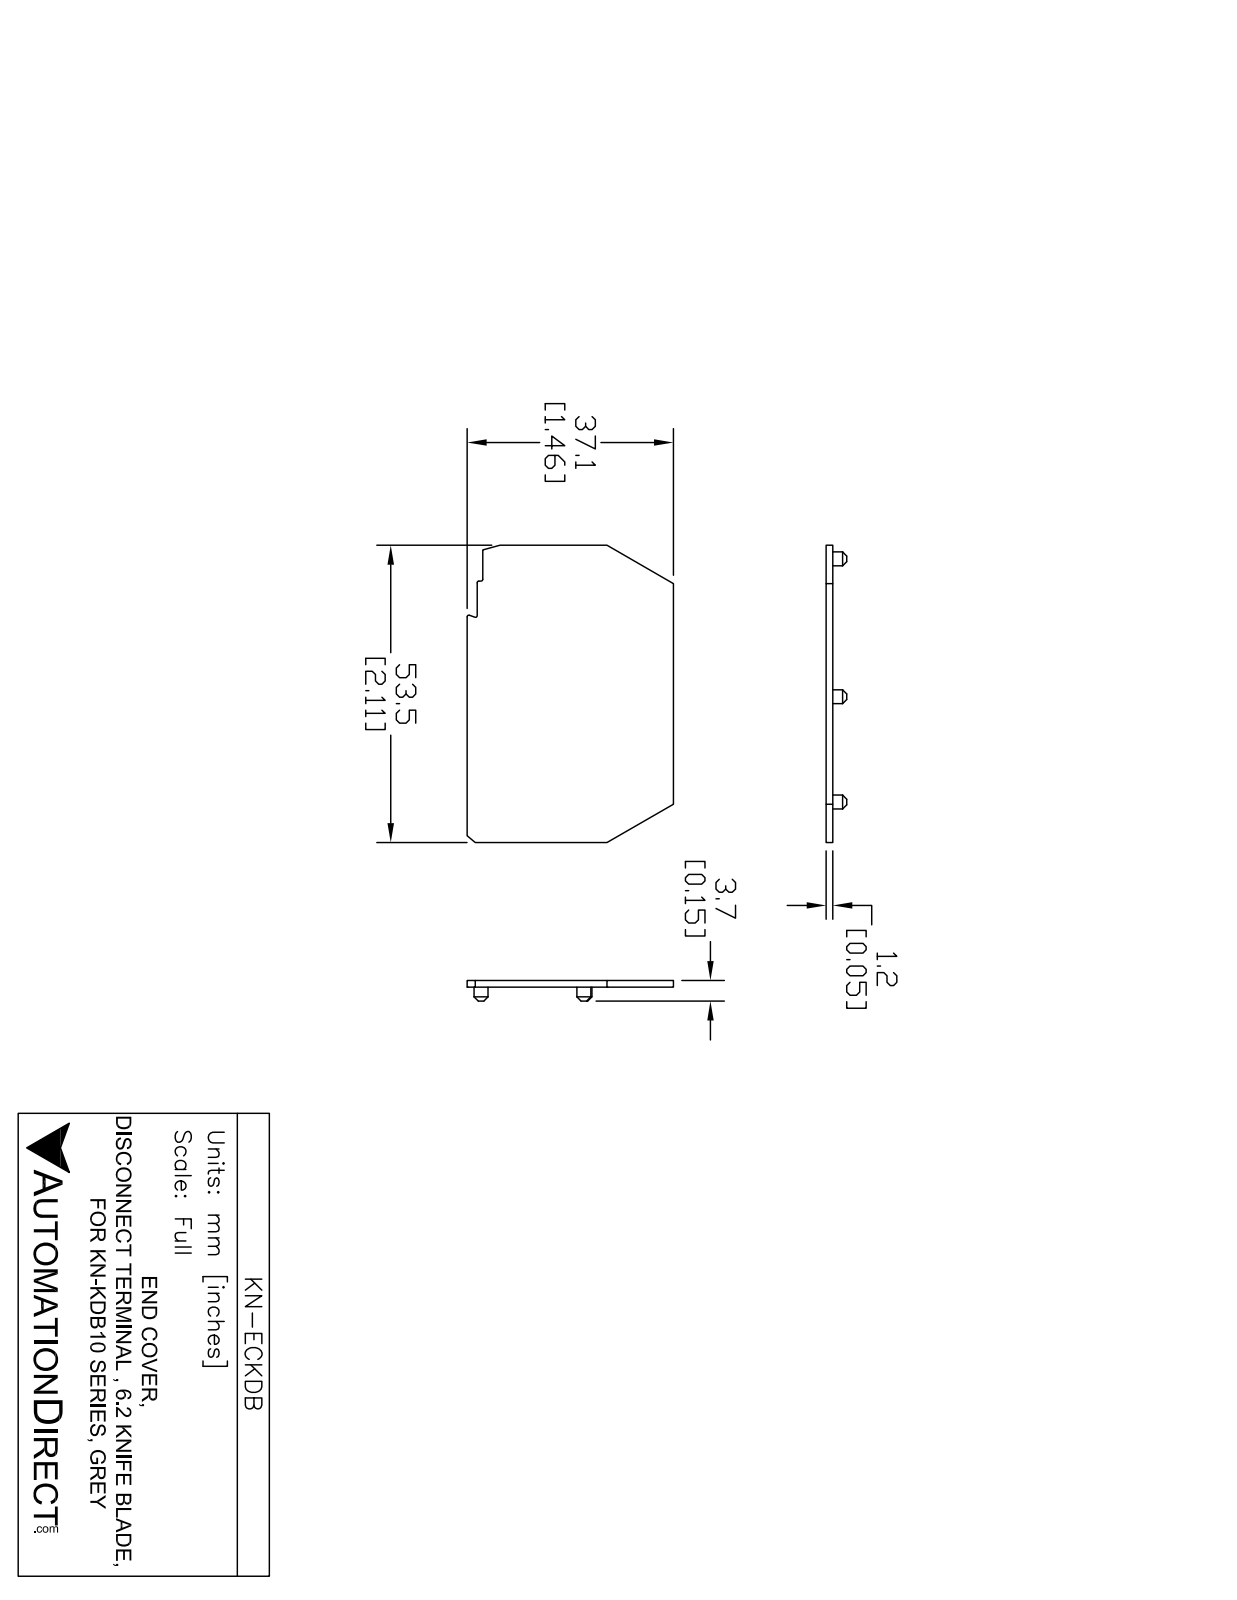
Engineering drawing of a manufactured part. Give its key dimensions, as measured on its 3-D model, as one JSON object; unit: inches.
{"part_name": "KN-ECKDB", "step_written_by": "SolidWorks 2014 (AUTOMOTIVE_DESIGN)", "units": "inches", "bodies": {"solids": 1, "faces": 40, "planar": 17, "cylindrical": 17, "other": 6}, "overall_size": [2.106, 1.461, 0.146], "volume_in3": 0.139, "surface_area_in2": 6.223, "round_holes": [[0.039, 3]], "round_bosses_or_shafts": [[0.098, 3]], "partial_cylinders_radius": [[0.012, 4]], "face_to_face_distances": [0.047, 1.461, 2.106, 0.071, 1.39, 0.111, 0.04, 1.35, 0.254, 1.852], "hole_center_spacings": [1.043, 1.222, 1.722]}
